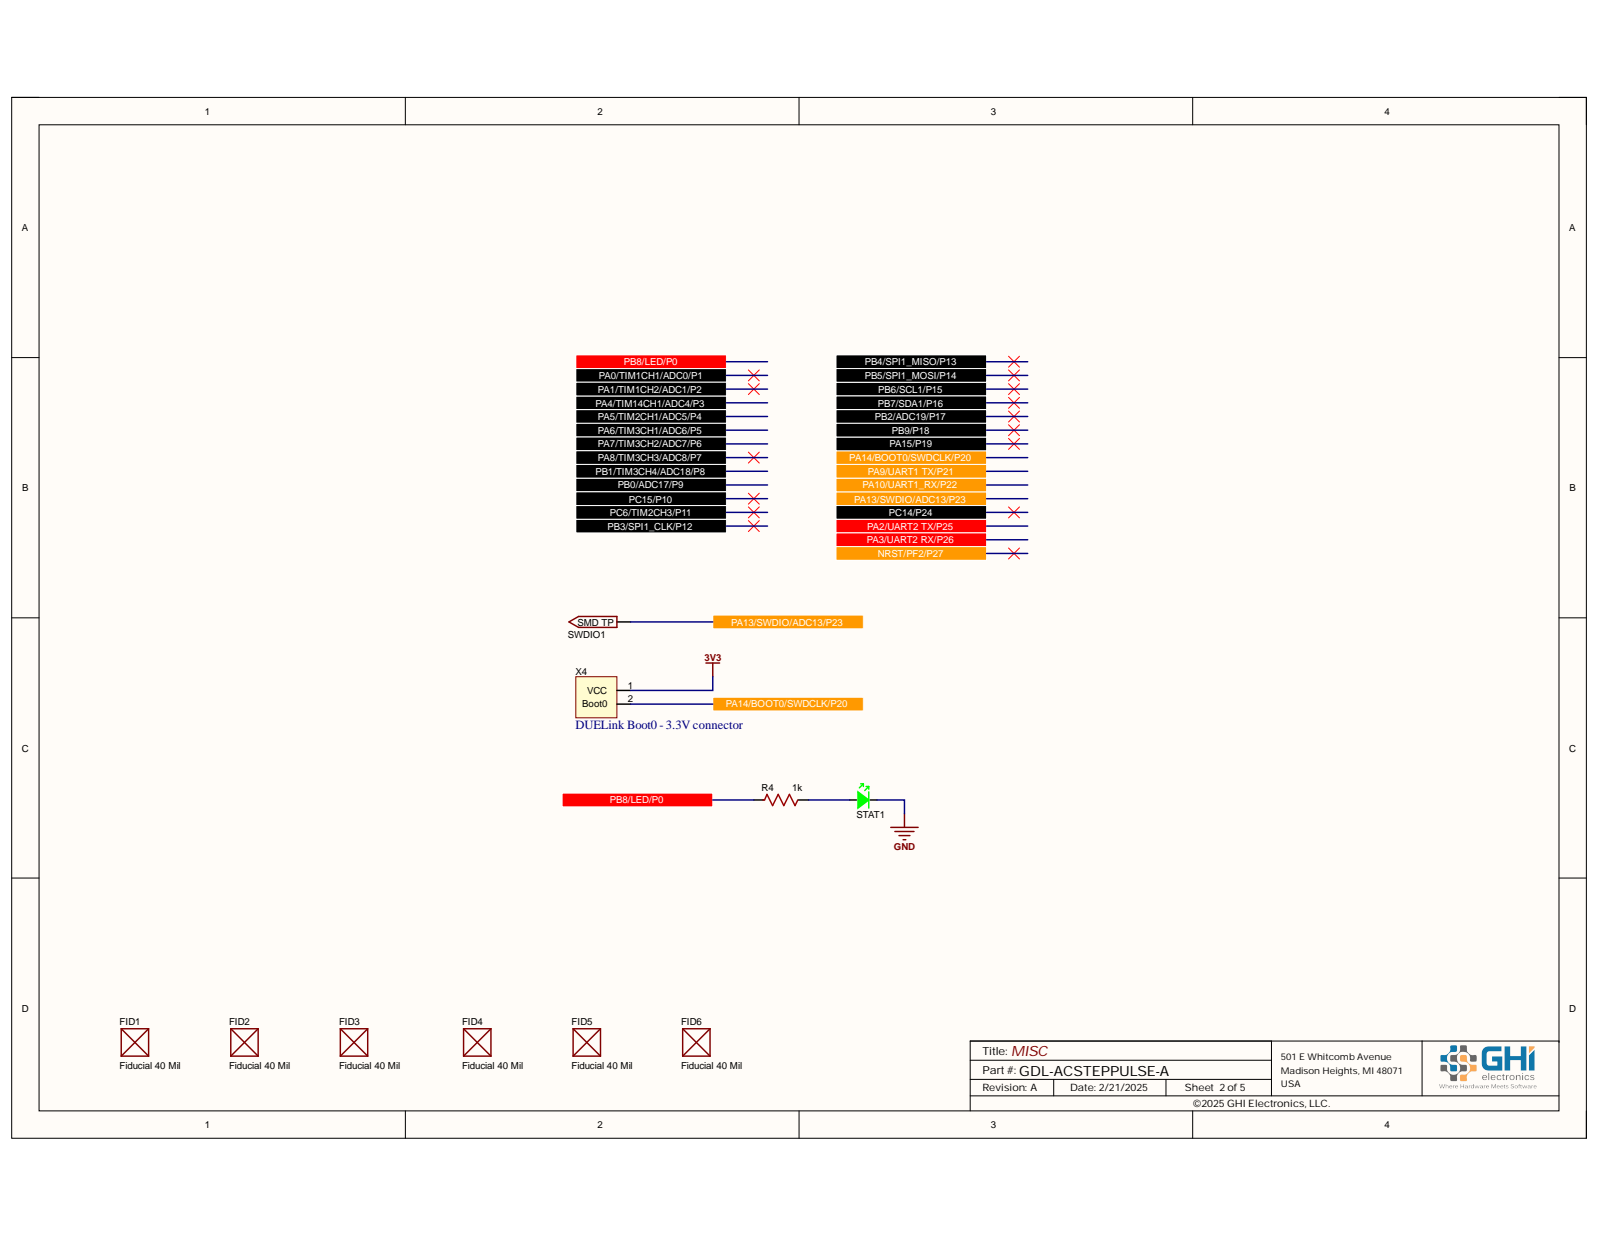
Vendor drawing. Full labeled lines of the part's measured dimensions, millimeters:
Part name (STEP PRODUCT): PCB; Board; STAT1; 0603 LED Green (+5 more)
STEP written by: Open CASCADE 7.5 (AUTOMOTIVE_DESIGN)
Units: millimetres
Bodies: 109 solids, 2148 faces (1565 planar, 420 cylindrical, 163 other)
Overall size (bounding box): 62 × 22 × 13.4
Volume: 4 571 mm³ · Surface area: 9 474 mm²
Round holes (diameter × count): ⌀3 ×13, ⌀0.6 ×9, ⌀1.3 ×9, ⌀2 ×9, ⌀2.75 ×9, ⌀3.5 ×9, ⌀1.02 ×2
Round bosses / shafts (diameter × count): ⌀2.5 ×9, ⌀1 ×9
Partial cylindrical surfaces — rounded edges, fillets, slot ends (radius × count): R0.8 ×36, R0.12 ×35, R0.2 ×18, R0.15 ×14, R0.47 ×9, R3.5 ×4, R0.1 ×2, R0.17 ×2
Main face-to-face distances: 1.6, 5, 15, 10, 4, 5.5, 9, 20, 1, 2.51
Hole centre spacings: 5, 15, 10, 5.94, 20, 10.5, 15.34, 25
